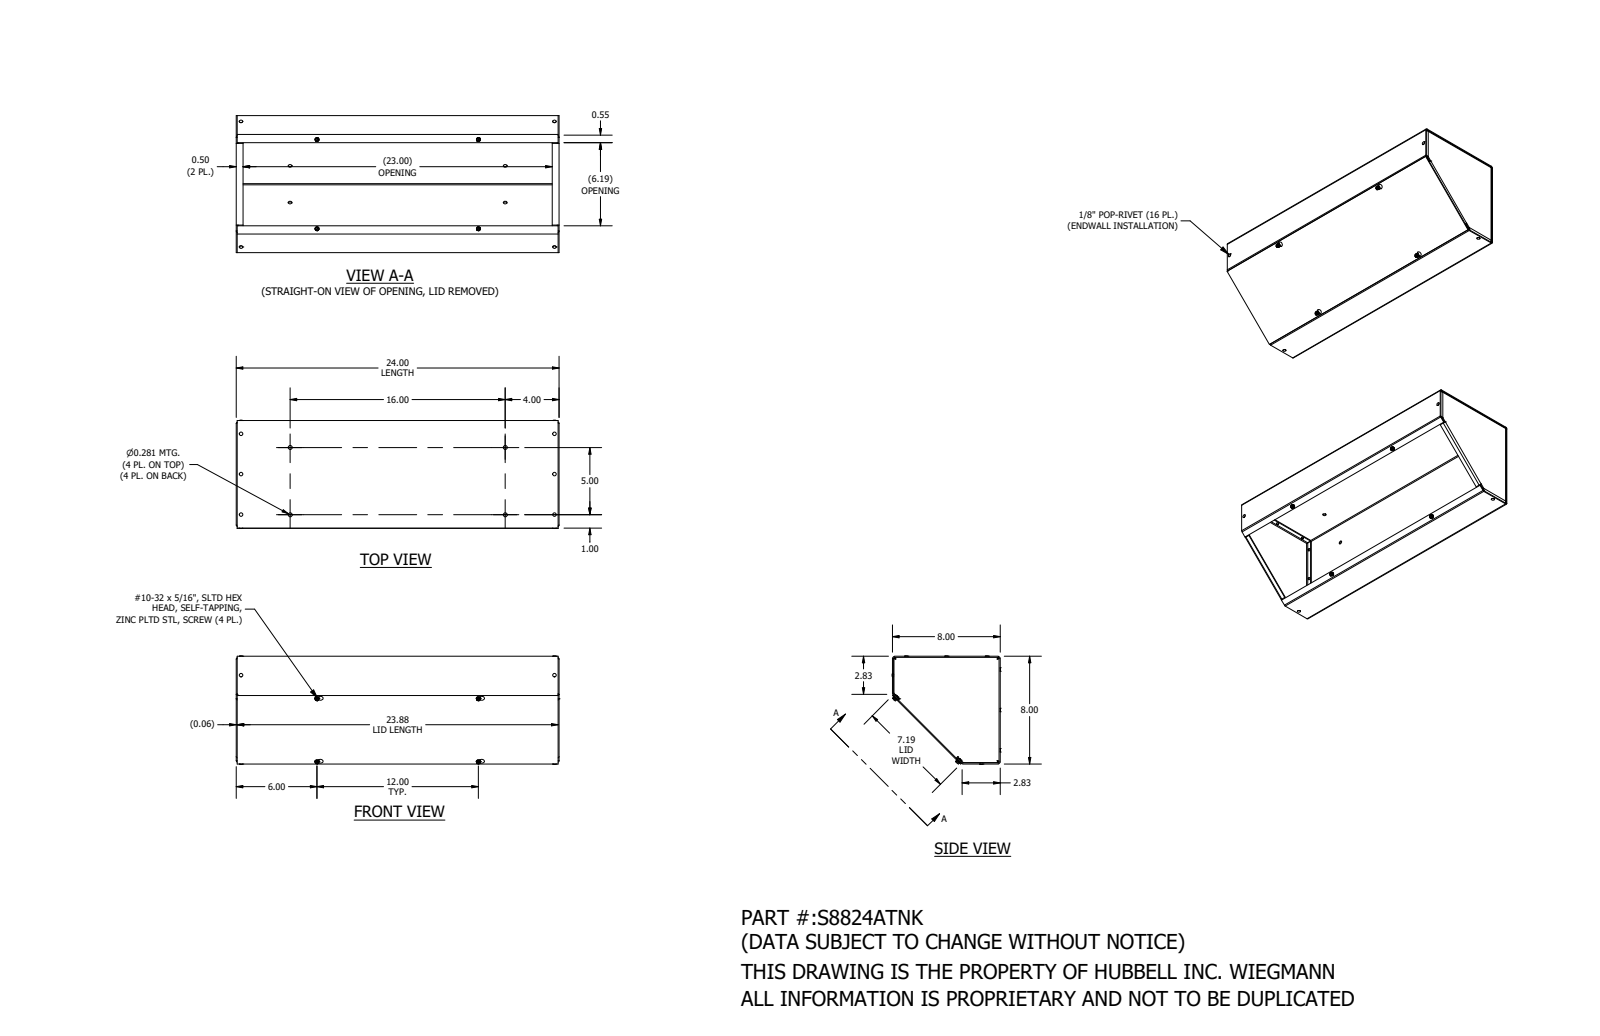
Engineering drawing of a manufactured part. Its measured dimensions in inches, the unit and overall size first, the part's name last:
Units: inches
Overall size (bounding box): 24 × 8.08 × 8.08
Round holes (diameter × count): ⌀0.129 ×16, ⌀0.281 ×8, ⌀0.171 ×4, ⌀0.406 ×4
Round bosses / shafts (diameter × count): ⌀0.262 ×16, ⌀0.125 ×15, ⌀0.313 ×4, ⌀0.181 ×4, ⌀0.125 ×1
Partial cylindrical surfaces — rounded edges, fillets, slot ends (radius × count): R0.064 ×32, R0.136 ×15, R0.063 ×12, R0.109 ×4, R0.062 ×3
Main face-to-face distances: 0.074, 7.926, 7.852, 8, 23.926, 0.068, 23.852, 24, 0.142, 0.148
Hole centre spacings: 3, 23.313, 23.505, 0.25, 0.415, 2.585, 3.656, 3.706
Volume: 60.93 in³ · Surface area: 1 668 in²
Bodies: 24 solids, 682 faces (268 planar, 178 cylindrical, 236 other)
Part name (STEP PRODUCT): S8824ATNK
STEP written by: SolidWorks 2021 (AUTOMOTIVE_DESIGN)
